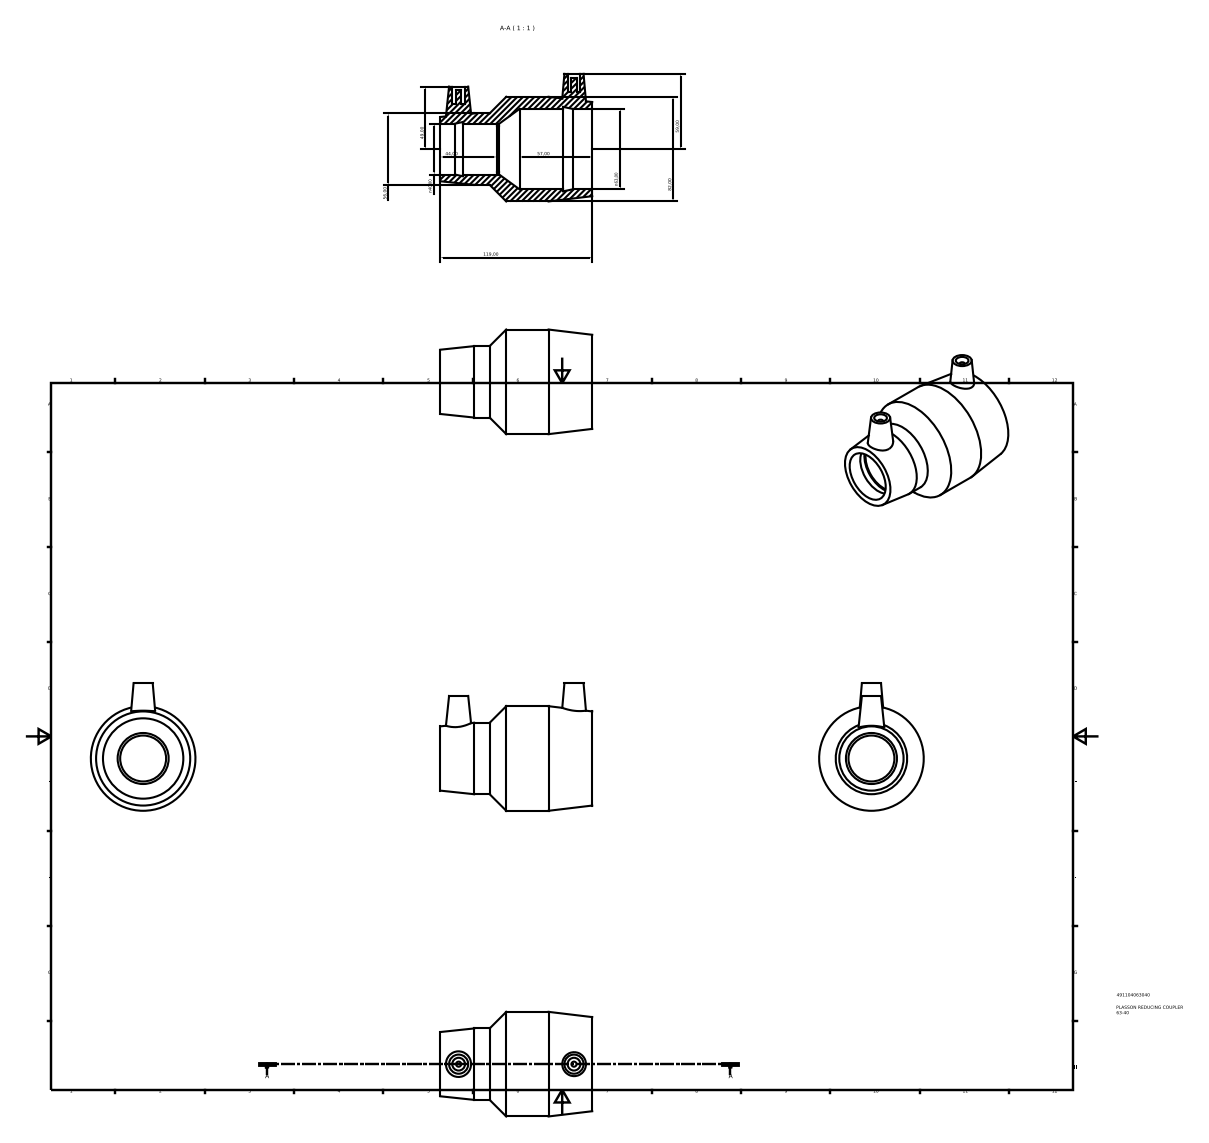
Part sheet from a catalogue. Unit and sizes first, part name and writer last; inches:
Units: inches
Overall size (bounding box): 4.685 × 3.937 × 3.228
Round holes (diameter × count): ⌀0.394 ×2, ⌀1.417 ×1, ⌀1.575 ×1, ⌀2.48 ×1
Round bosses / shafts (diameter × count): ⌀0.157 ×2, ⌀3.228 ×1, ⌀2.205 ×1
Main face-to-face distances: 4.685, 3.787, 0.898, 1.819, 1.969, 2.866, 1.732, 0.087, 2.055, 2.953
Hole centre spacings: 3.561
Volume: 13.07 in³ · Surface area: 83.79 in²
Bodies: 1 solid, 31 faces (12 planar, 11 cylindrical, 8 other)
Part name (STEP PRODUCT): 491104063040
STEP written by: Autodesk Inventor 2015 (AUTOMOTIVE_DESIGN)
